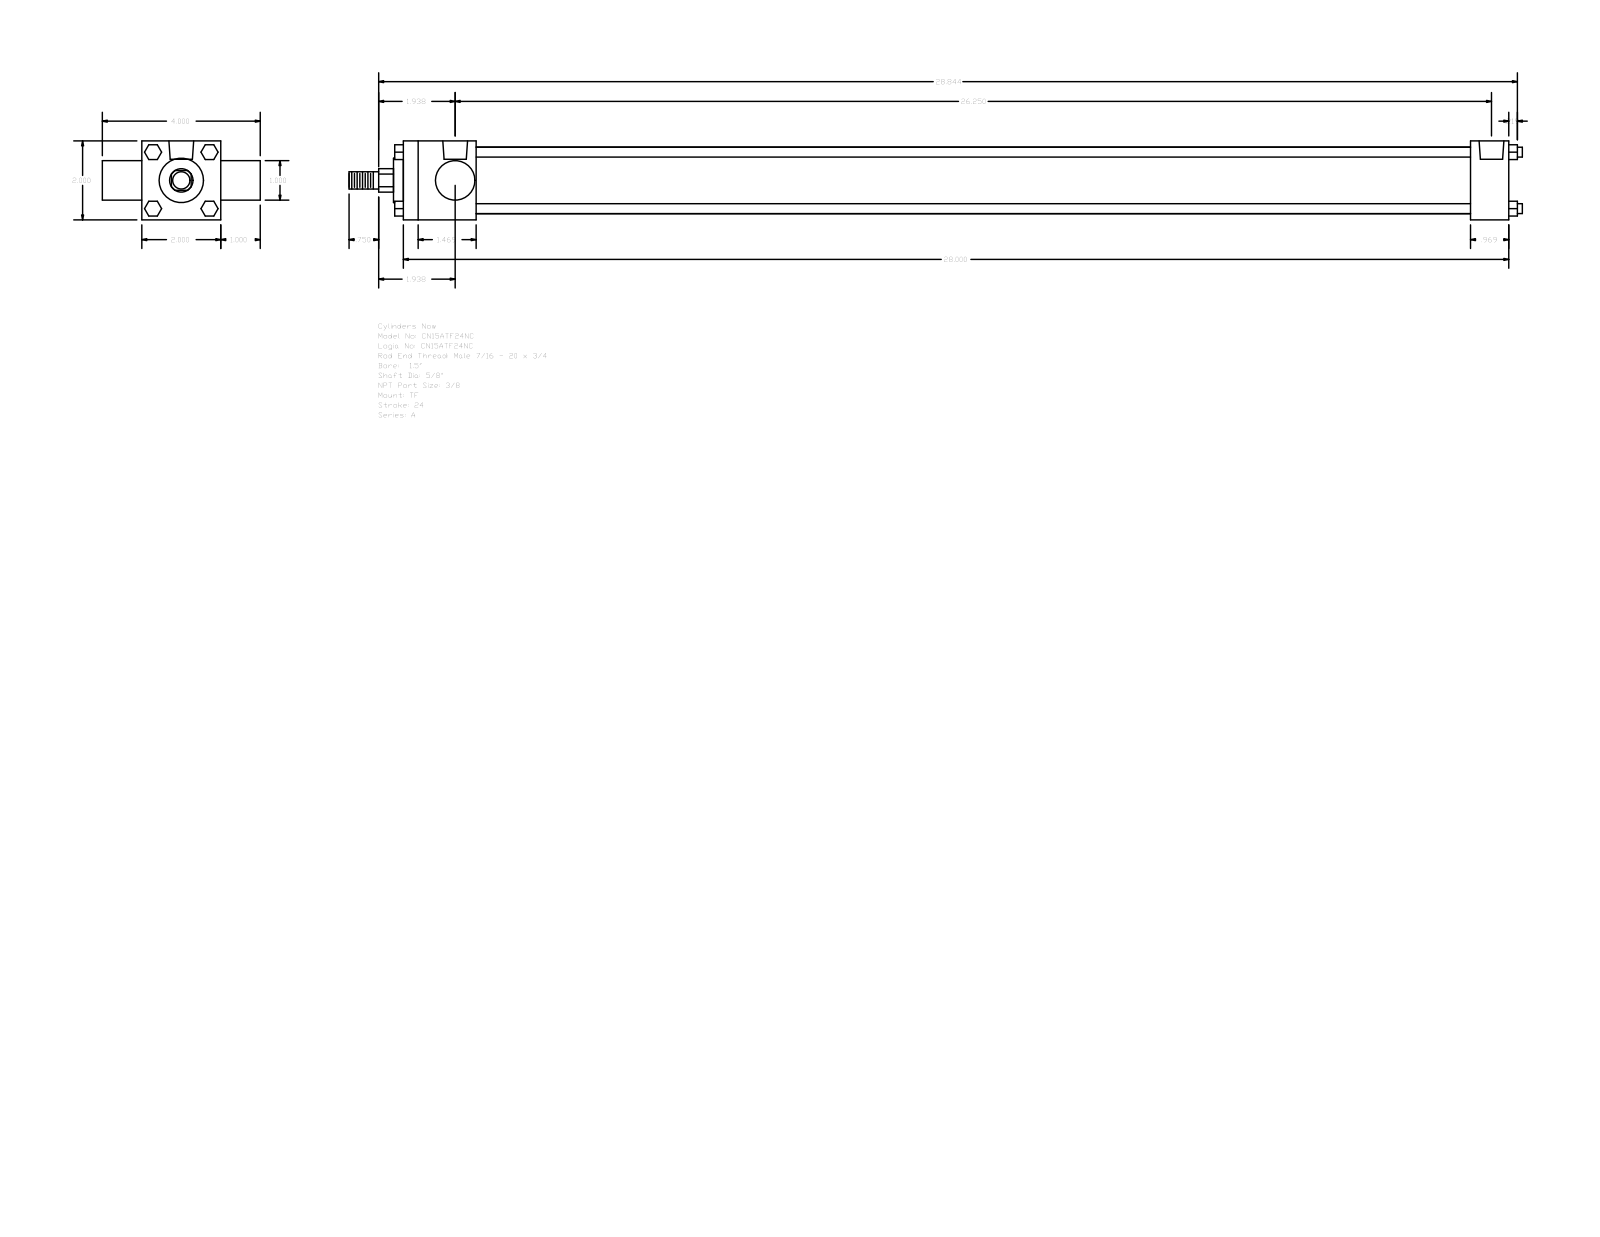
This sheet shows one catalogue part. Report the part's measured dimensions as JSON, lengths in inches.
{"part_name": "A_TF__0150_0.625", "step_written_by": "GSSL Pune (CONFIG_CONTROL_DESIGN)", "units": "inches", "bodies": {"solids": 0, "faces": 120, "planar": 92, "cylindrical": 28, "other": 0}, "overall_size": [29.719, 4, 2], "round_holes": [[0.219, 3], [0.627, 2]], "round_bosses_or_shafts": [[0.25, 4], [1.69, 1], [1.125, 1], [1, 1], [0.625, 1], [0.437, 1]], "partial_cylinders_radius": [[0.297, 1]], "face_to_face_distances": [2, 28, 1, 3, 1.844, 27.031, 25.187, 26.156, 0.969, 4], "hole_center_spacings": [0.156, 26.094, 25.937, 26.25]}
